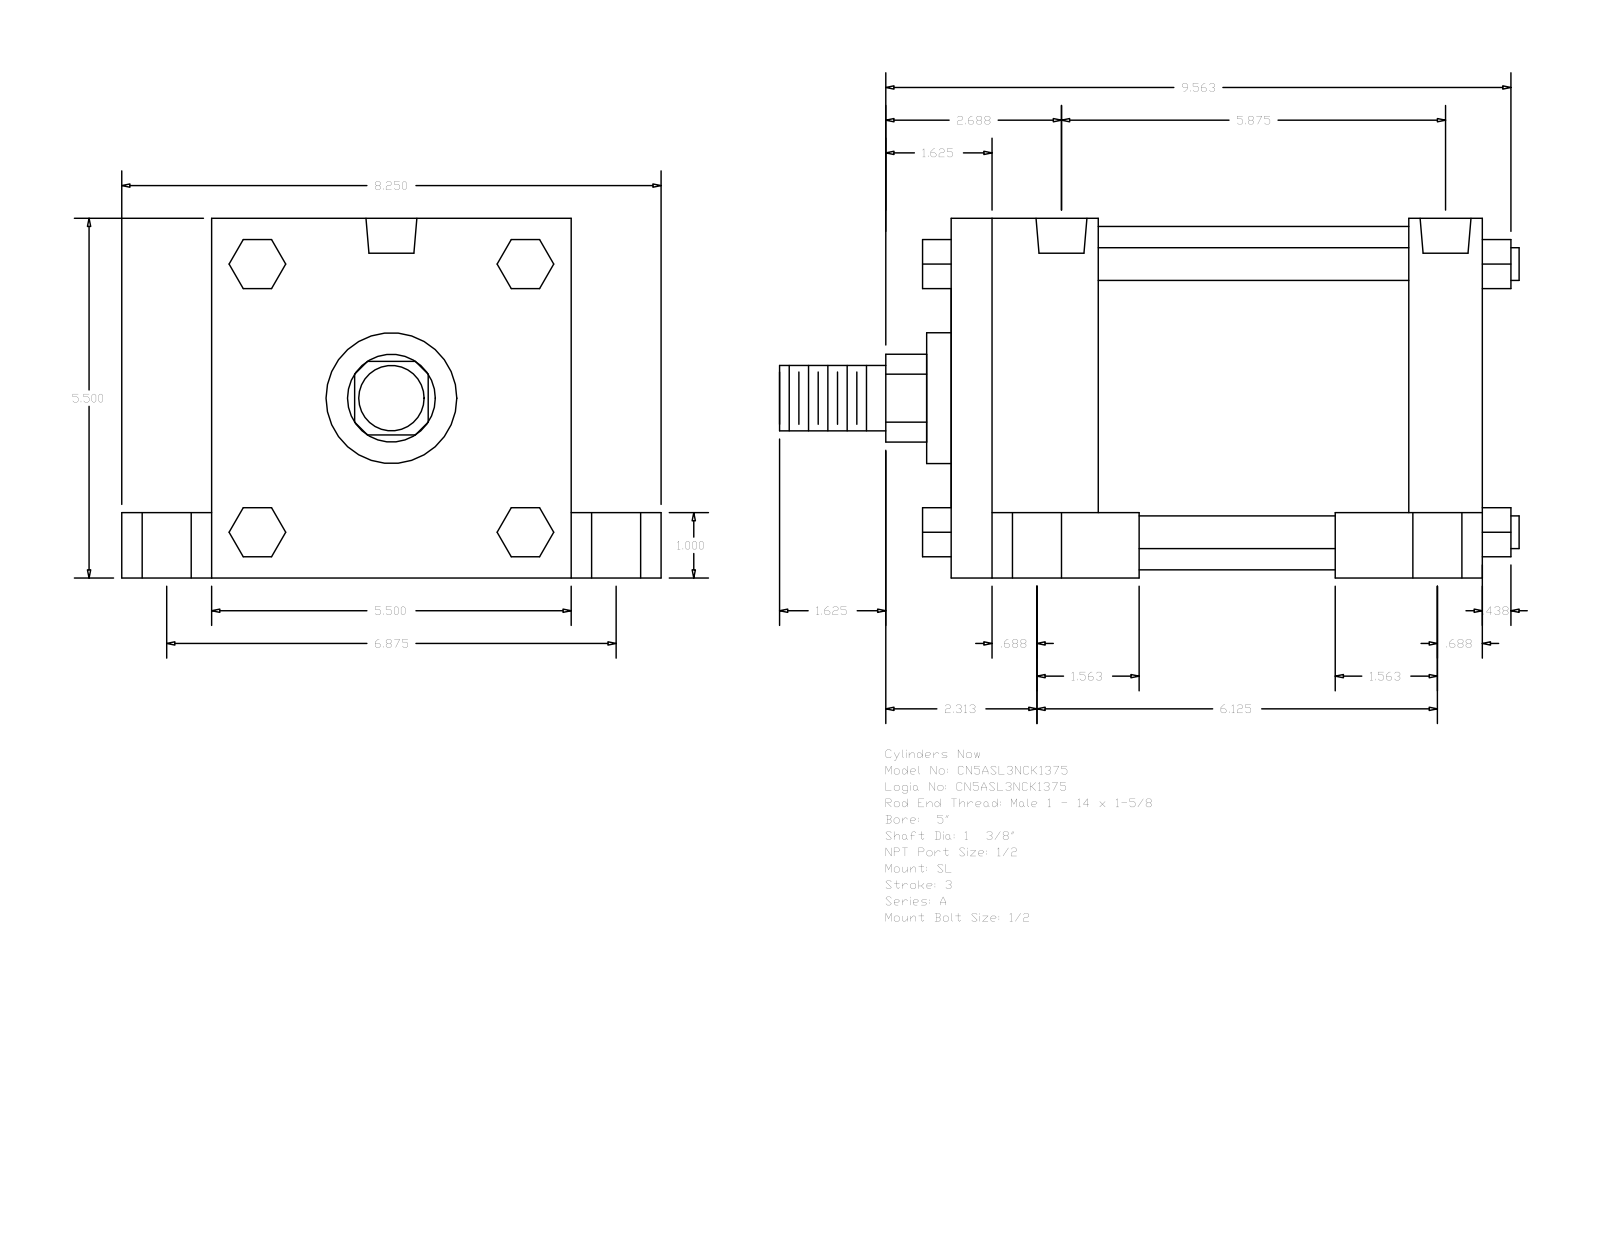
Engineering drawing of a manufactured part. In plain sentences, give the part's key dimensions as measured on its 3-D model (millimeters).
The part is named "A_SL__0500_1.375". Its 3-D file was written by "GSSL Pune (CONFIG_CONTROL_DESIGN)". It is 0 solids with 150 faces: 114 planar, 36 cylindrical and 0 other. Overall it measures 287.34 by 209.55 by 139.7 millimeters. Round holes: 4 of diameter 8.73, 4 of diameter 19.05, 4 of diameter 25.4, 2 of diameter 19.77. Round bosses or shafts: 4 of diameter 12.7, 1 of diameter 133.35, 1 of diameter 50.8, 1 of diameter 34.92, 1 of diameter 25.4. Partial cylindrical surfaces (rounded edges, fillets, slot ends): 1 of radius 17.06. The main face-to-face distances are 139.7, 206.38, 57.15, 28.58, 25.4, 114.3, 34.93, 174.63, 177.8, 120.65. The hole center spacings are 2.39, 87.31, 87.37, 87.83, 88.12, 144.45, 146.84, 155.57.
